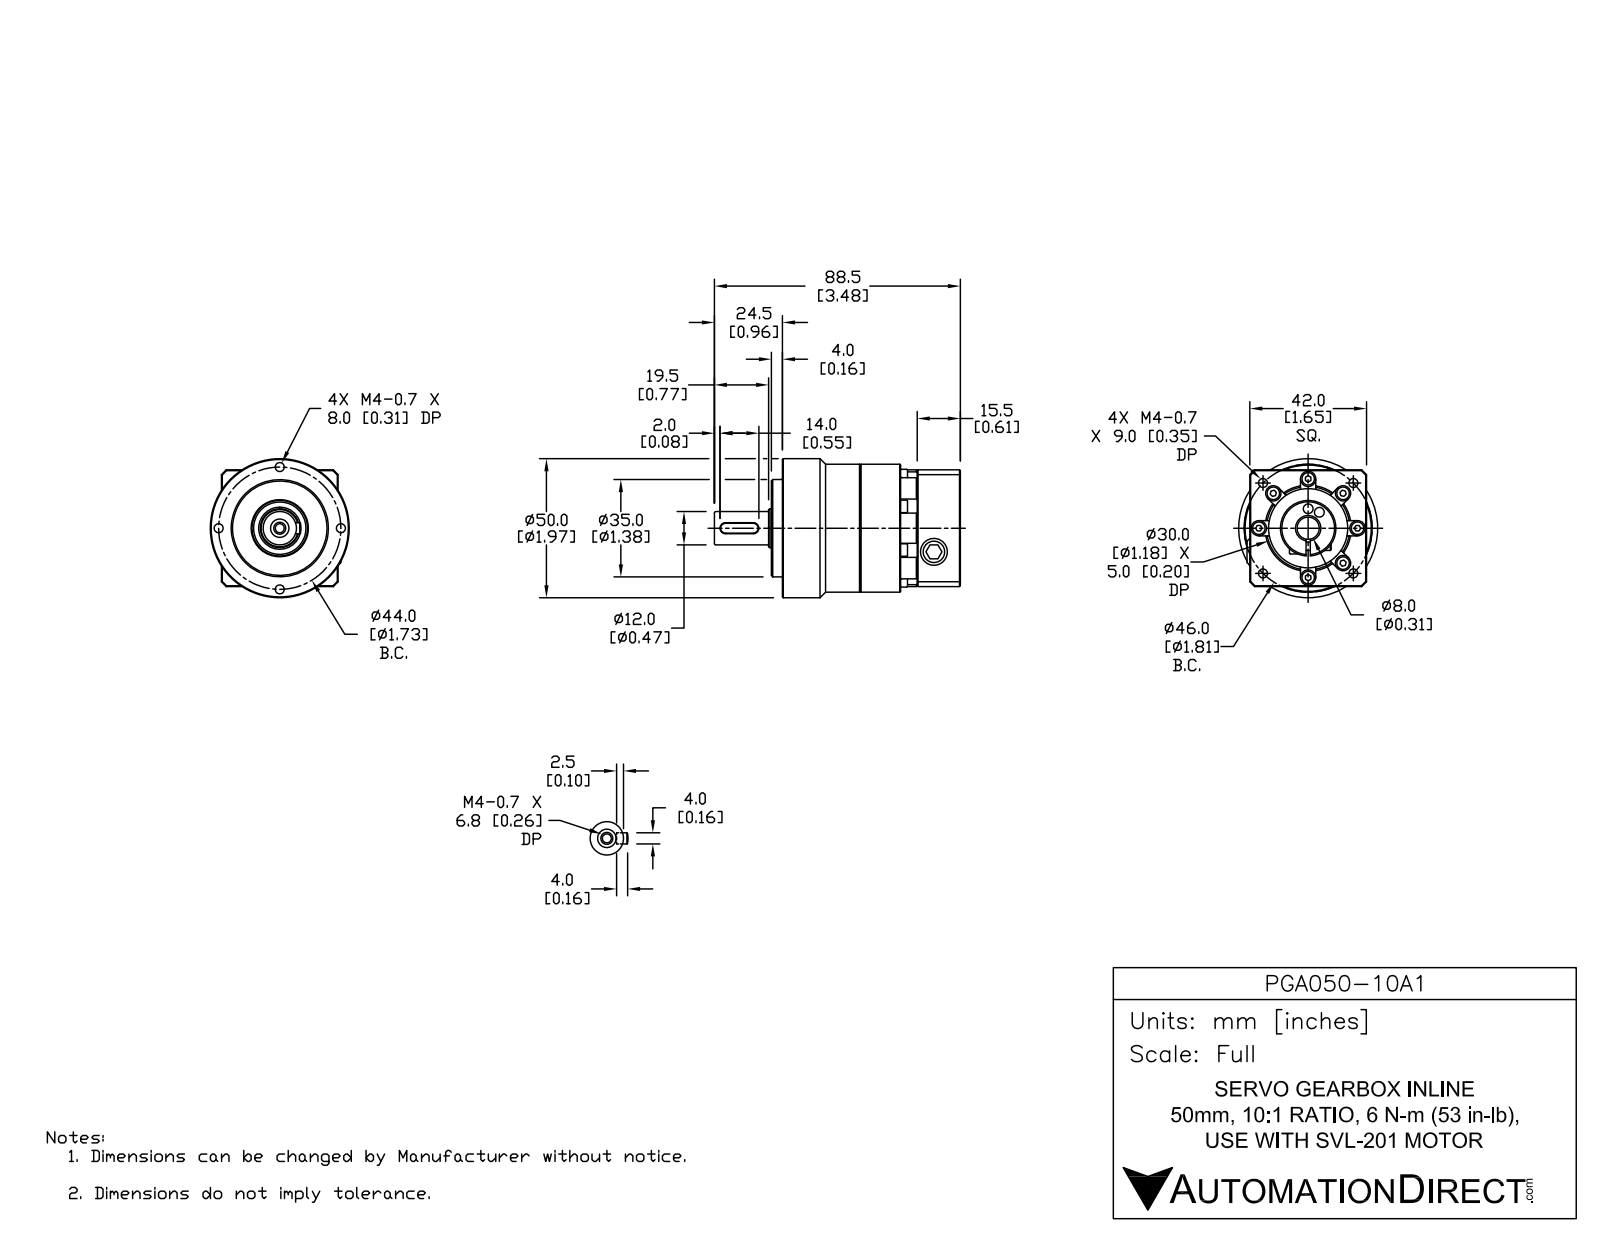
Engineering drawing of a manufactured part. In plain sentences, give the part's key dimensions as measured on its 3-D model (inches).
The part is named "PGA050-10A1". Its 3-D file was written by "SolidWorks 2014 (AUTOMOTIVE_DESIGN)". It is 1 solid with 570 faces: 229 planar, 159 cylindrical and 182 other. Overall it measures 3.484 by 1.969 by 1.969 inches. Its volume is 6.391 cubic inches and its surface area 34.84 square inches. Round holes: 9 of diameter 0.128, 7 of diameter 0.11, 7 of diameter 0.217, 3 of diameter 0.138, 1 of diameter 0.169, 1 of diameter 0.315, 1 of diameter 0.787, 1 of diameter 1.122. Round bosses or shafts: 15 of diameter 0.177, 7 of diameter 0.098, 1 of diameter 1.969, 1 of diameter 1.811, 1 of diameter 1.378, 1 of diameter 0.551, 1 of diameter 0.472, 1 of diameter 0.217. Partial cylindrical surfaces (rounded edges, fillets, slot ends): 8 of radius 0.108, 2 of radius 0.079, 1 of radius 0.048, 1 of radius 0.128, 1 of radius 0.157, 1 of radius 0.591, 1 of radius 0.827, 1 of radius 1.122. The main face-to-face distances are 1.654, 1.909, 0.61, 2.52, 0.157, 2.677, 2.067, 0.197, 0.413, 0.236. The hole center spacings are 0.643, 0.679, 1.113, 1.484, 1.637, 0.699, 0.535, 0.619.
